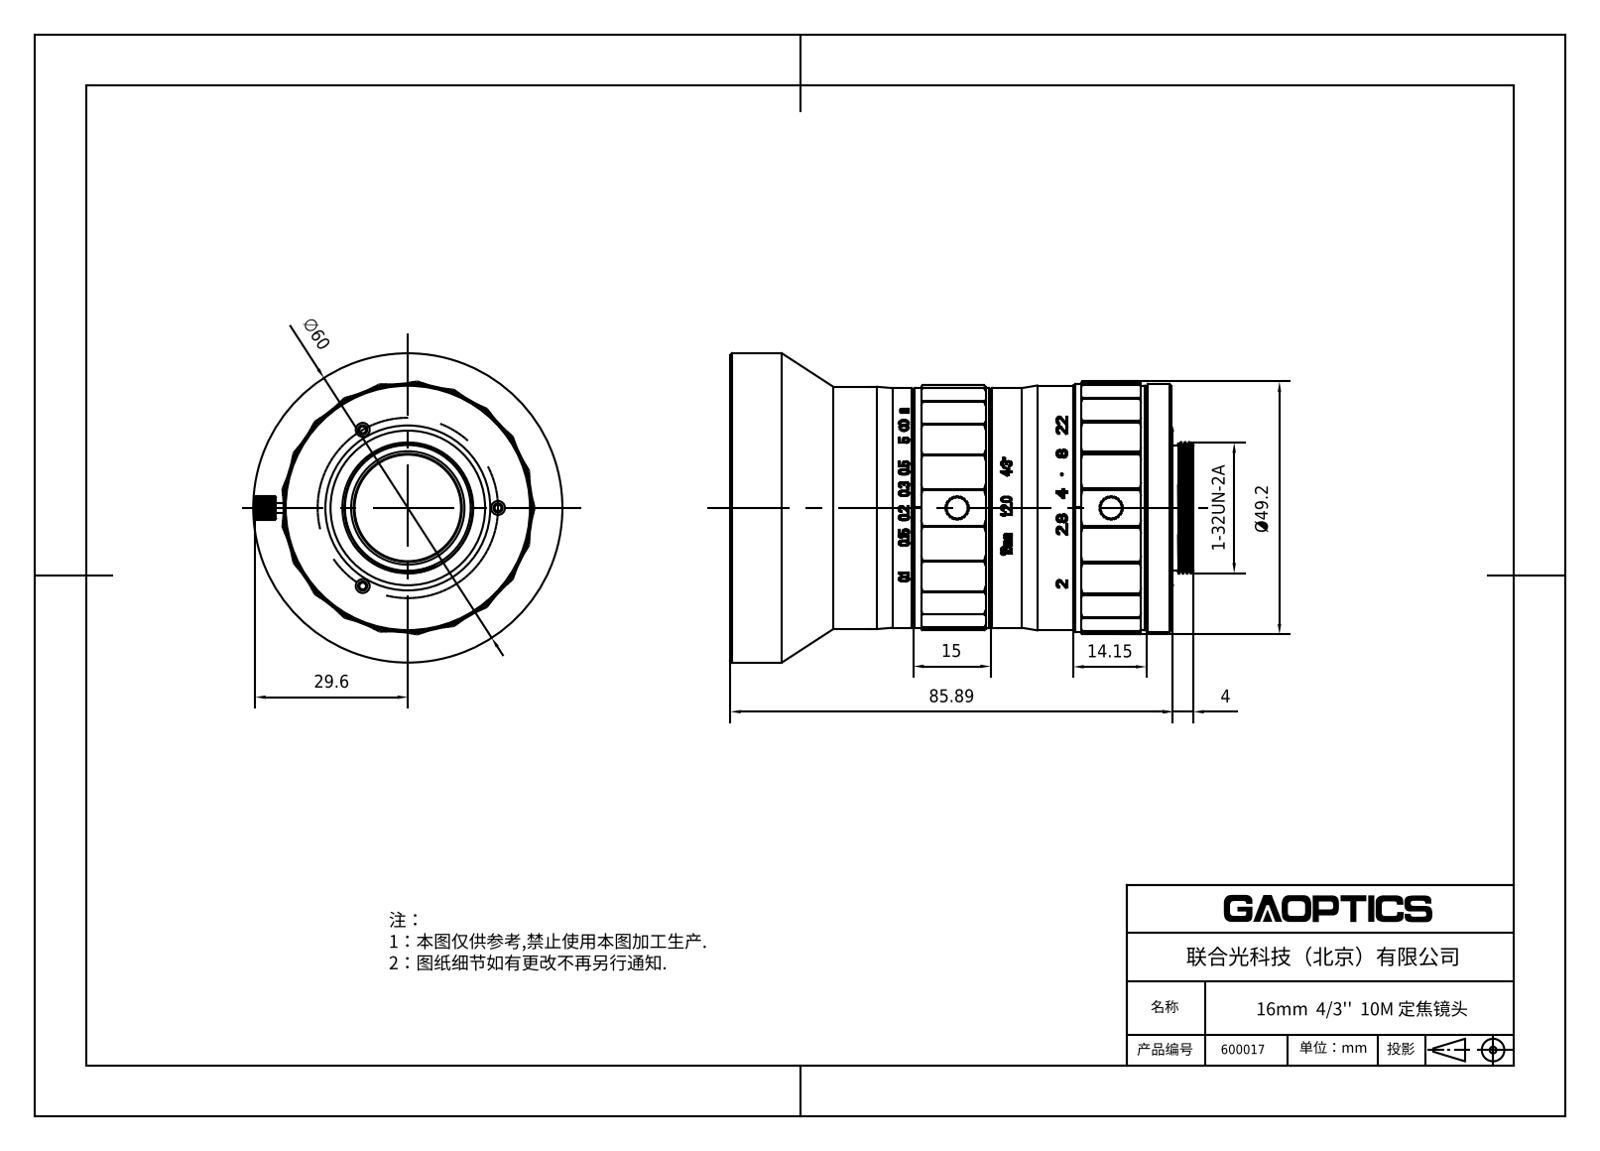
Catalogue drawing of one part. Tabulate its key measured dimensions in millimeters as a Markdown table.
| quantity | value |
| --- | --- |
| part name | 600017 |
| STEP written by | SolidWorks 2020 (CONFIG_CONTROL_DESIGN) |
| units | millimeters |
| bodies | 0 solids, 2121 faces (1027 planar, 426 cylindrical, 668 other) |
| overall size | 89.89 × 60 × 60 |
| round holes (diameter × count) | 1.3 × 9, 1.8 × 6, 2 × 6, 1.6 × 4, 1.9 × 3, 2.7 × 3, 2.8 × 3, 1.4 × 2, 21 × 1, 22 × 1, 24.2 × 1, 30 × 1 |
| round bosses / shafts (diameter × count) | 60 × 1, 55 × 1, 53 × 1, 48 × 1, 47.5 × 1, 47.4 × 1, 47 × 1, 46.96 × 1 |
| partial cylindrical surfaces (radius × count) | 1.46 × 42, 0.39 × 21, 21 × 21, 26 × 21, 1.5 × 4, 0.65 × 3, 0.9 × 3, 1.4 × 3 |
| main face-to-face distances | 2.01, 76.96, 74.95, 75.25, 1.7, 75.26, 73.25, 0.32, 1.69, 74.94 |
| hole center spacings | 22.04, 26.88, 4.05, 13.45, 17.5, 30.63, 42.25, 42.86 |
